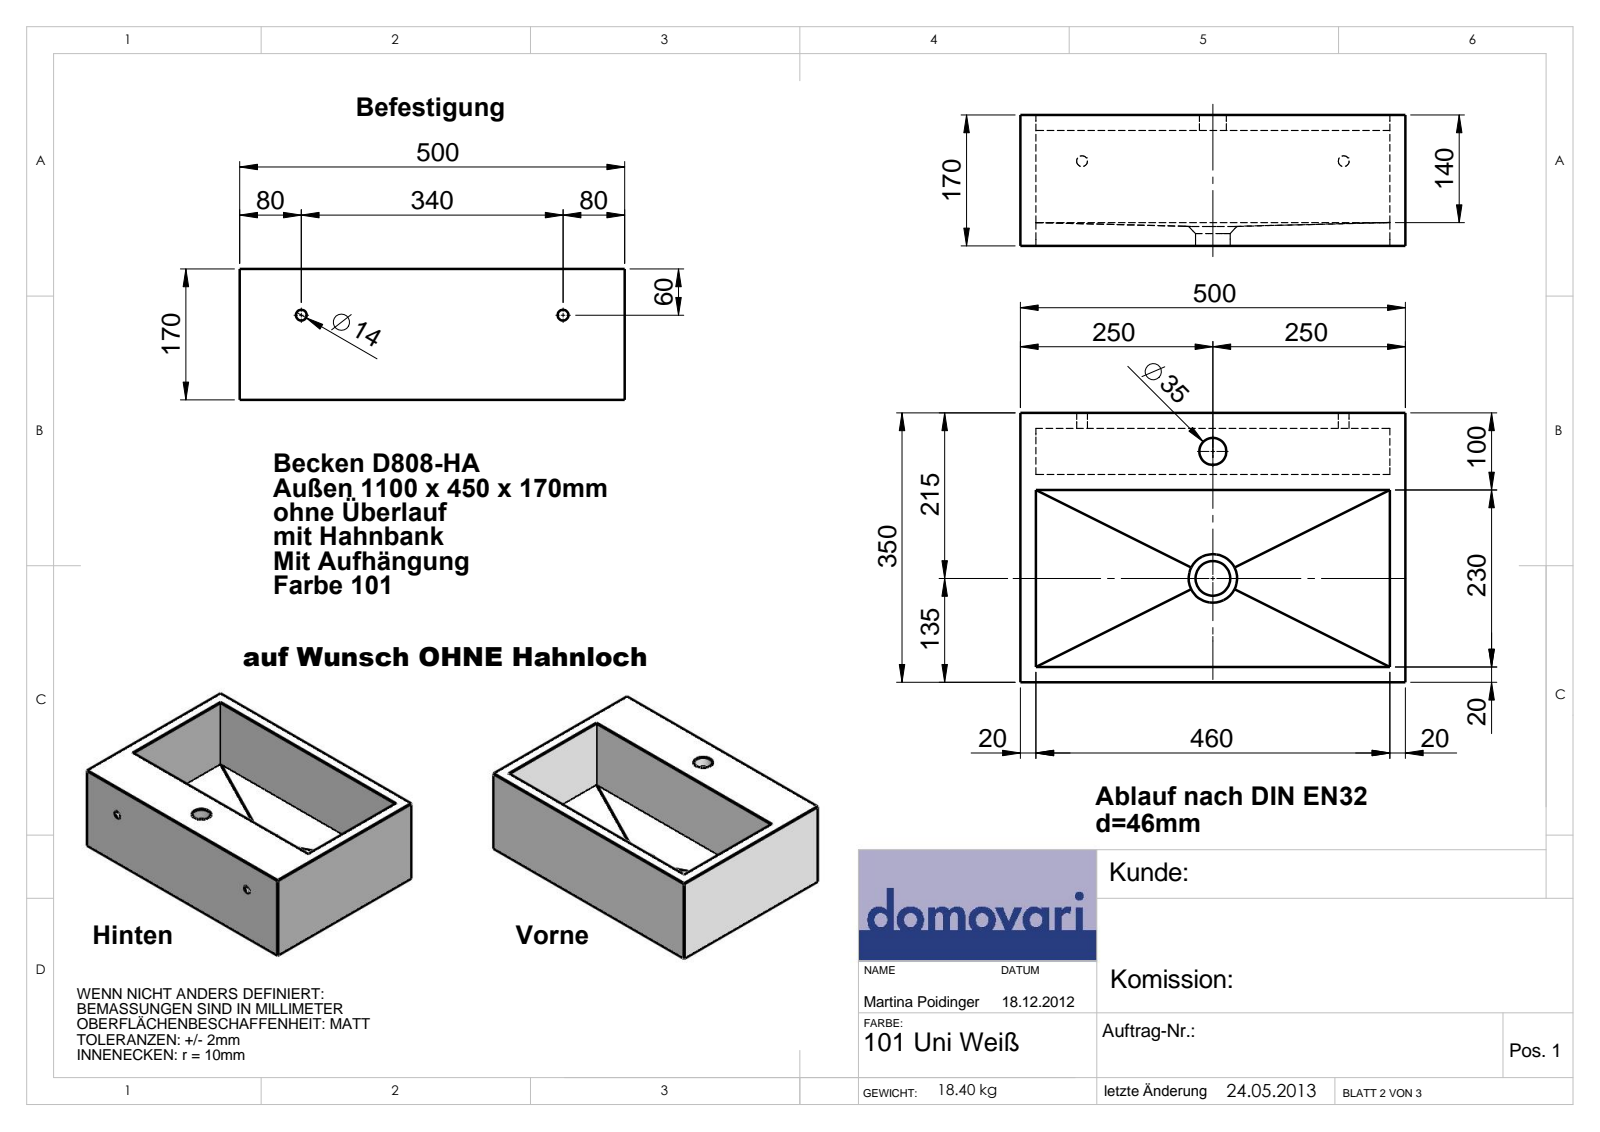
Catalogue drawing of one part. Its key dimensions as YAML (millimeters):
part_name: "D808-HA"
step_written_by: "SolidWorks 2017 (AUTOMOTIVE_DESIGN)"
units: millimeters
bodies: {solids: 0, faces: 33, planar: 15, cylindrical: 8, other: 10}
overall_size: [500, 350, 170]
round_holes:
  - {diameter: 14, count: 2}
  - {diameter: 35, count: 1}
  - {diameter: 45, count: 1}
face_to_face_distances: [20, 80, 330, 250, 350, 480, 270, 60, 170, 100]
hole_center_spacings: [165, 340]
